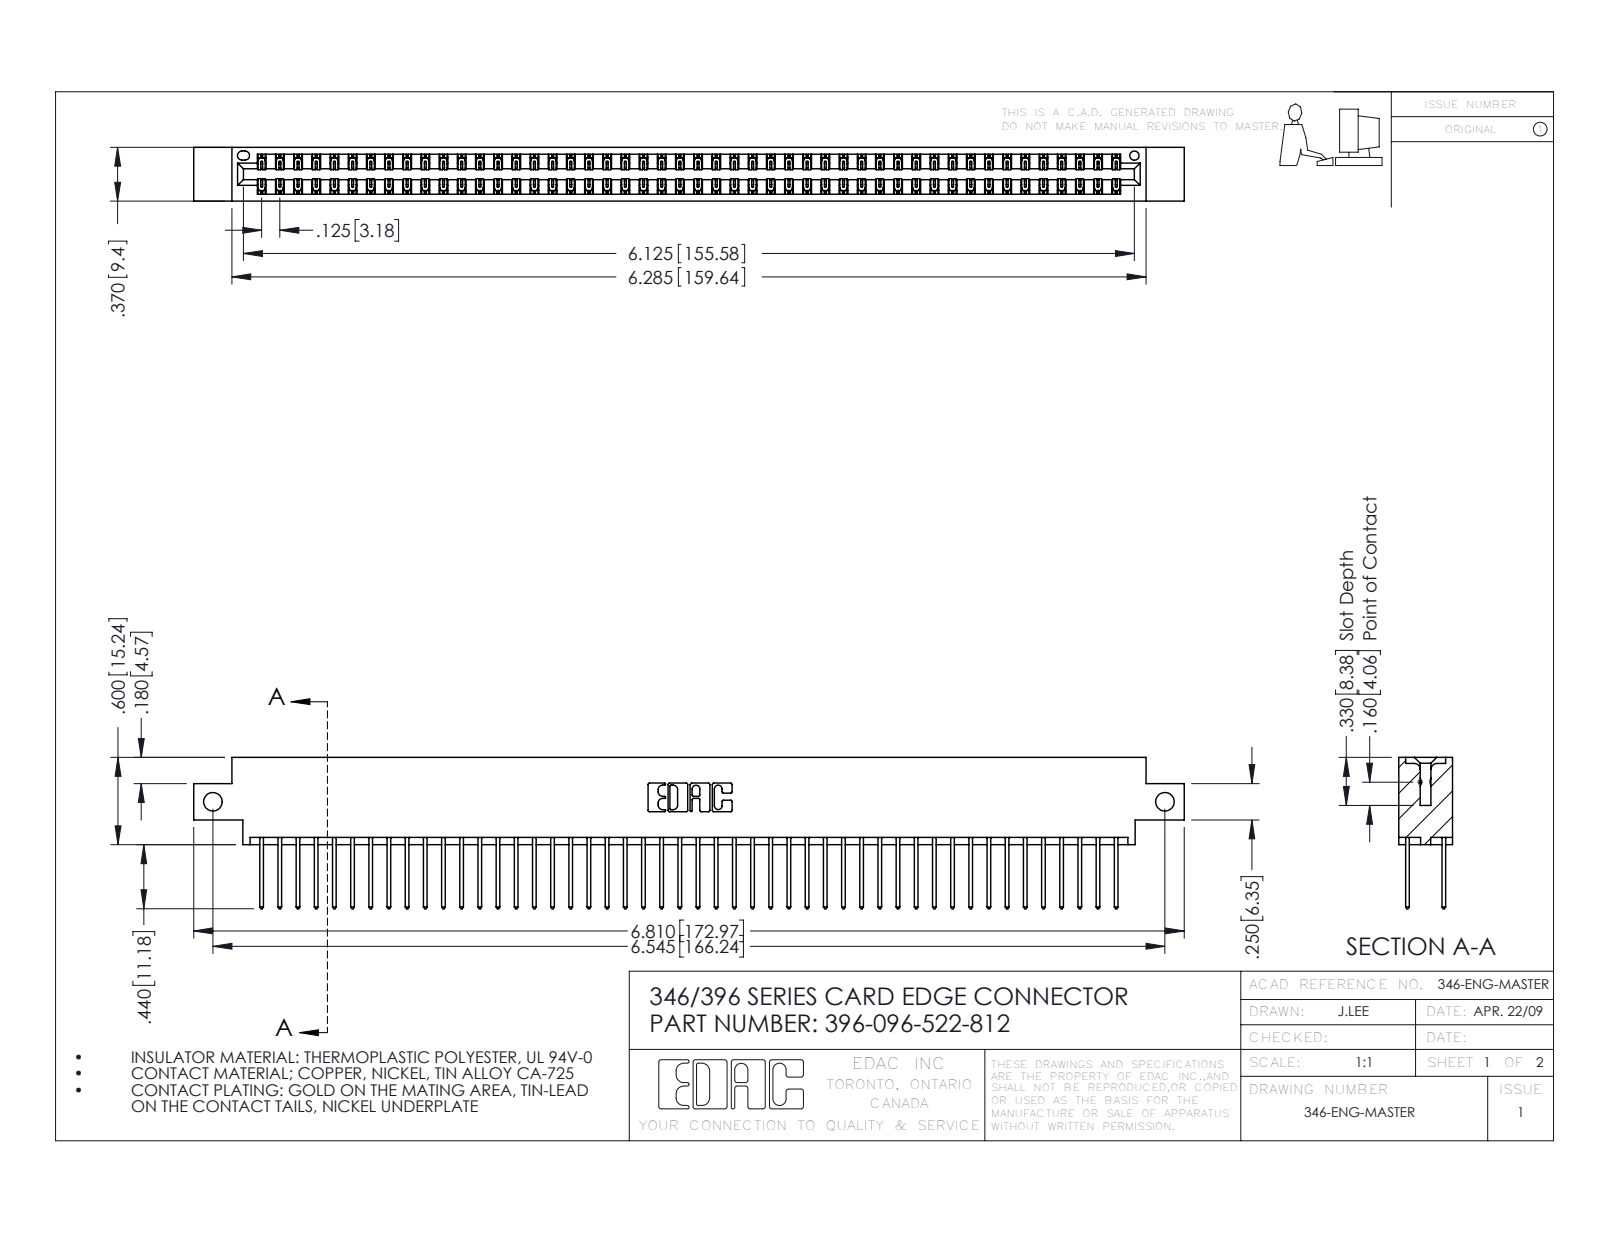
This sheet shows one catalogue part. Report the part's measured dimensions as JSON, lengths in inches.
{"part_name": "396-096-522-812; 345-292-001_345-293-122; 346 Part_0.170 Offset - Side Mount", "step_written_by": "SolidWorks 2016 (CONFIG_CONTROL_DESIGN)", "units": "inches", "bodies": {"solids": 97, "faces": 5118, "planar": 3440, "cylindrical": 1678, "other": 0}, "overall_size": [6.81, 1.04, 0.37], "volume_in3": 1.032, "surface_area_in2": 38.02, "round_holes": [[0.128, 2], [0.064, 1]], "partial_cylinders_radius": [[0.006, 144], [0.01, 96], [0.01, 22], [0.007, 6], [0.031, 6], [0.026, 3], [0.014, 2], [0.022, 2]], "face_to_face_distances": [0.048, 0.322, 0.25, 0.37, 0.072, 0.298, 0.025, 0.275, 0.148, 0.222], "hole_center_spacings": [6.545]}
